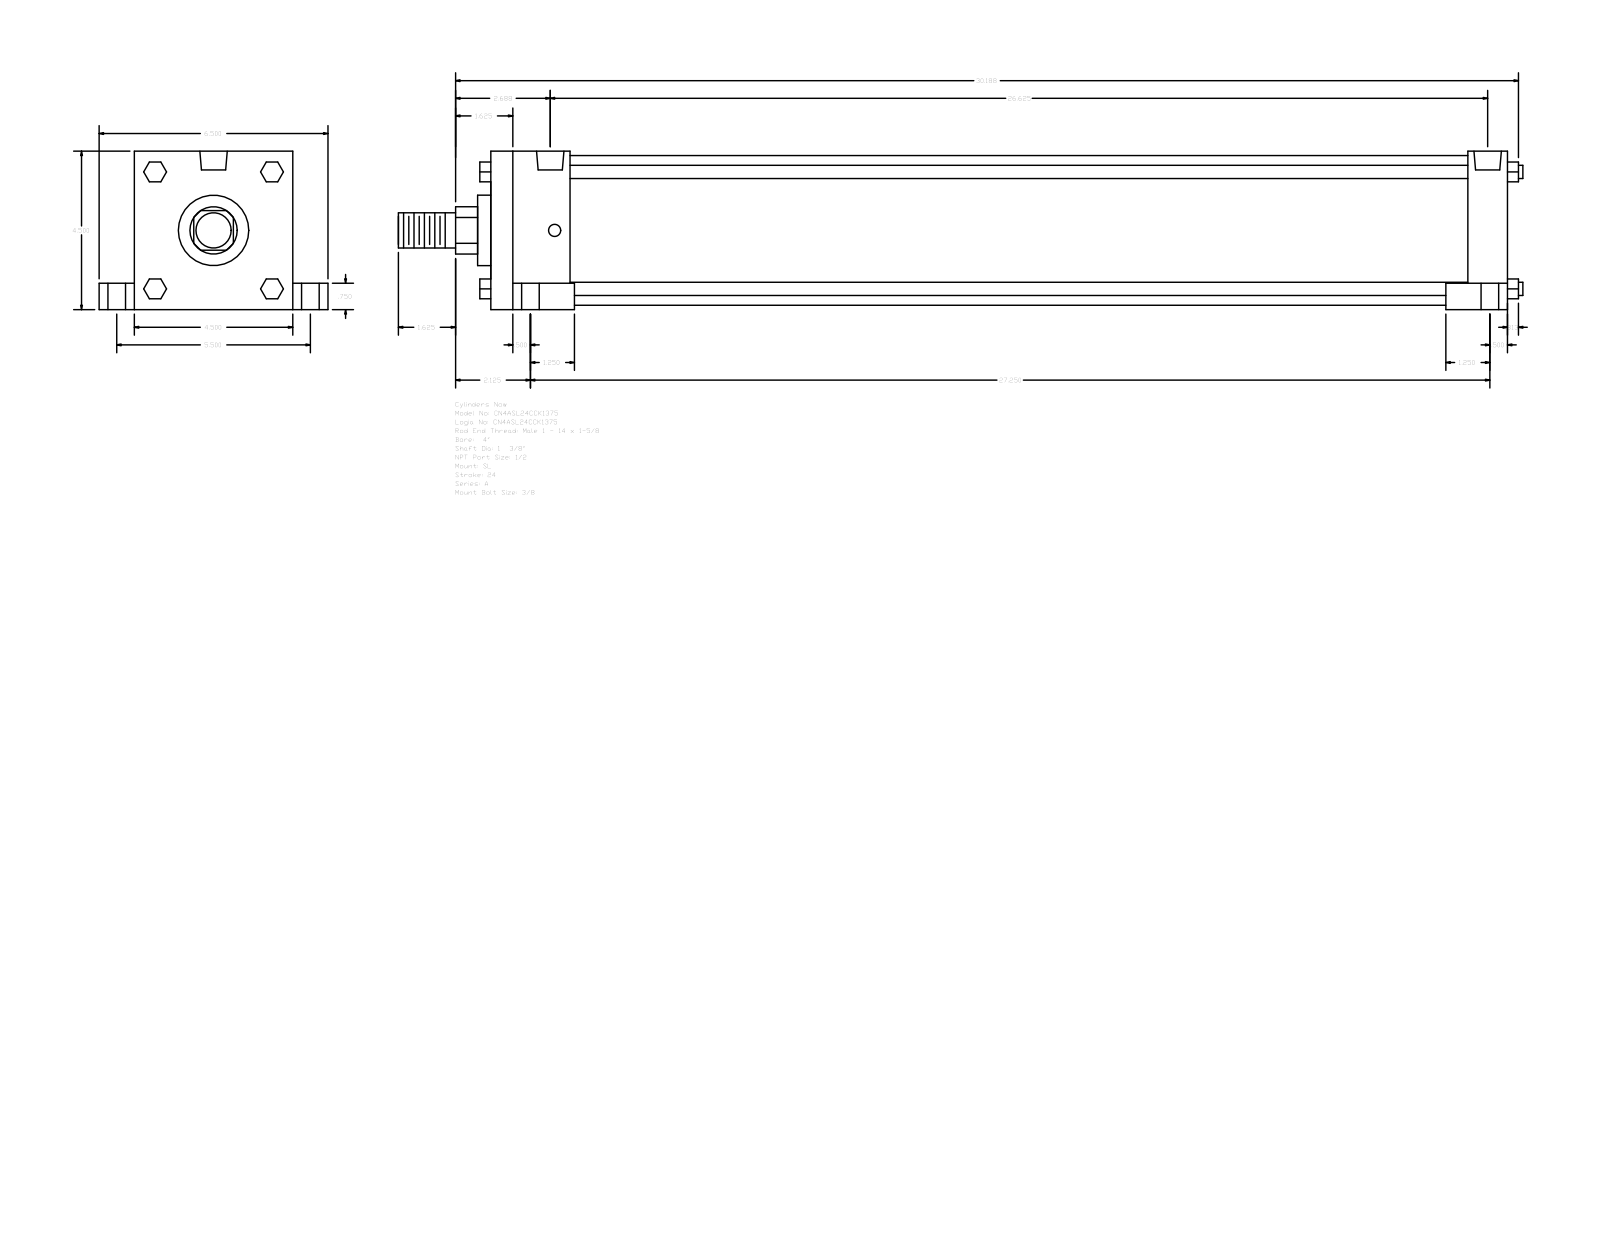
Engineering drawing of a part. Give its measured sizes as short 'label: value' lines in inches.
name: A_SL__0400_1.375
written by: GSSL Pune (CONFIG_CONTROL_DESIGN)
unit: in
bodies: 0 solids, 150 faces (114 planar, 36 cylindrical, 0 other)
size: 31.937 × 6.5 × 4.5
holes: 4× ⌀0.344, 4× ⌀0.5, 4× ⌀0.75, 2× ⌀0.778
bosses: 4× ⌀0.375, 1× ⌀4.25, 1× ⌀2, 1× ⌀1.375, 1× ⌀1
rounds: 1× R0.672
face distances: 4.5, 28.875, 2.25, 1.125, 1, 26.625, 27.75, 25.5, 5.5, 0.75
hole spacings: 0.125, 2.751, 2.756, 2.807, 2.835, 5.5, 26.375, 26.5
